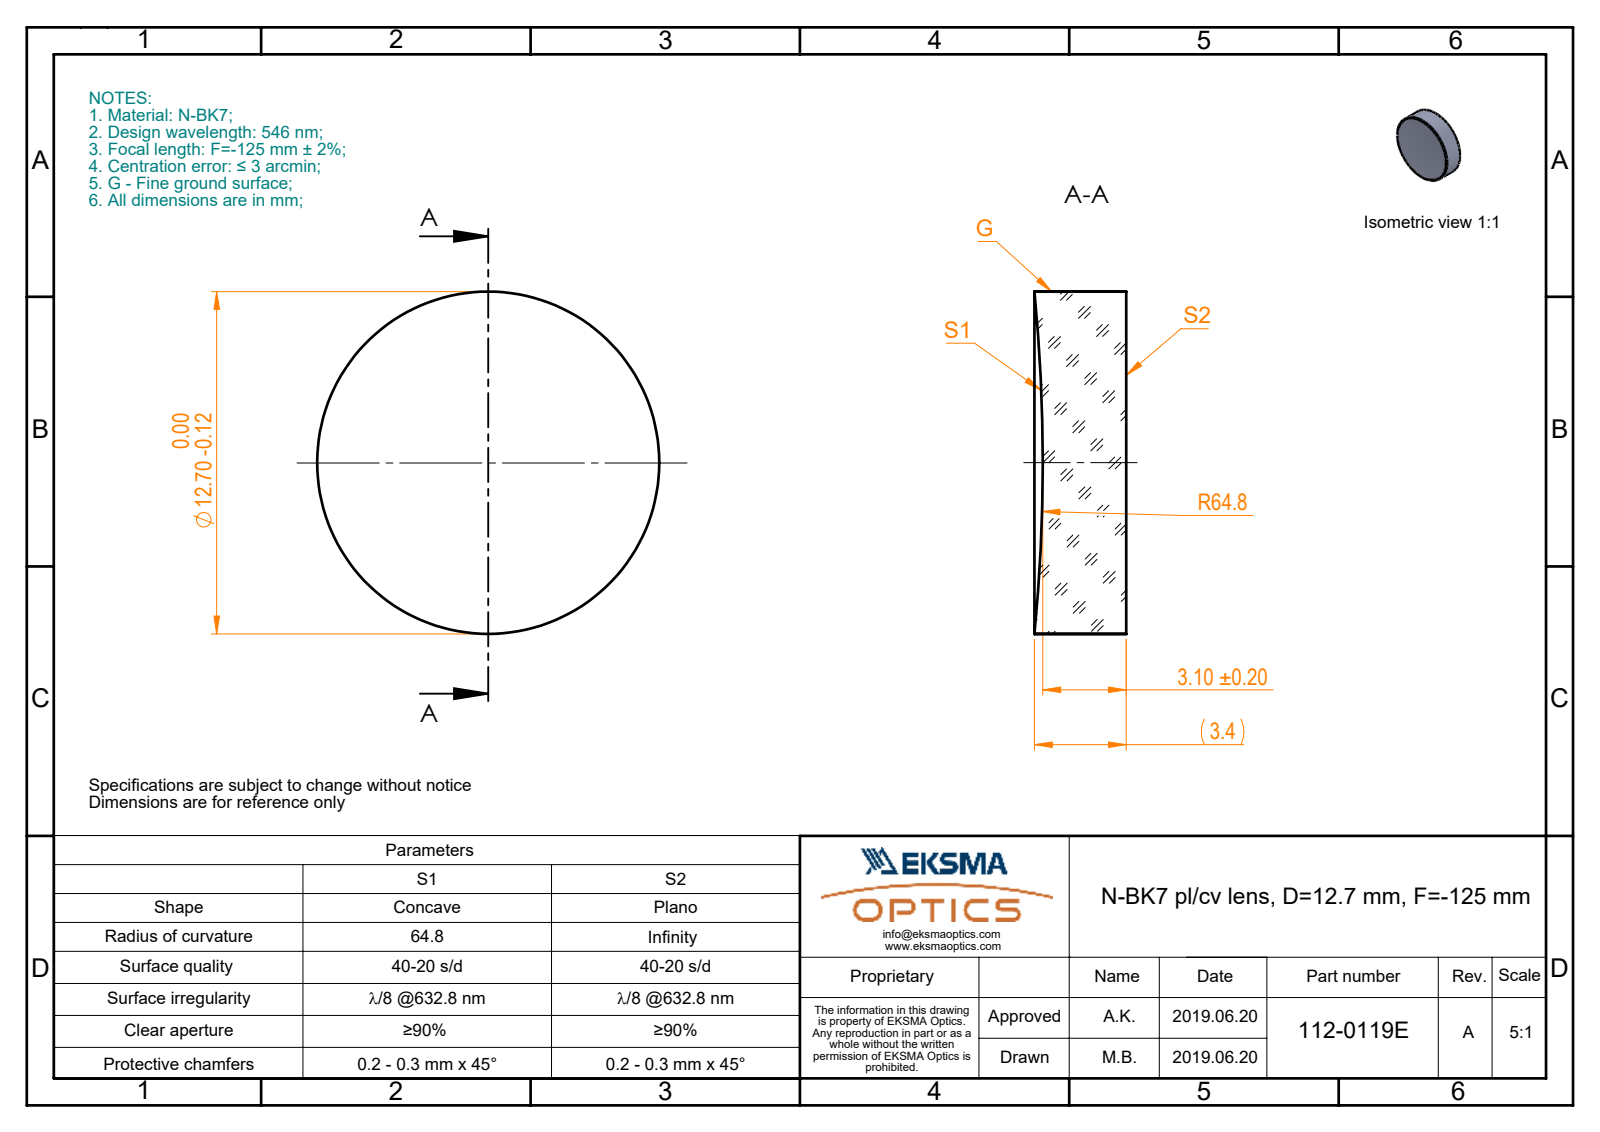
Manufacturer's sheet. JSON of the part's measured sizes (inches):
{"part_name": "112-0119E BK7 pl-cv 12.7 F-125", "step_written_by": "SolidWorks 2017 (CONFIG_CONTROL_DESIGN)", "units": "inches", "bodies": {"solids": 1, "faces": 5, "planar": 1, "cylindrical": 2, "other": 2}, "overall_size": [0.5, 0.5, 0.134], "volume_in3": 0.025, "surface_area_in2": 0.605, "round_bosses_or_shafts": [[0.5, 1]]}
